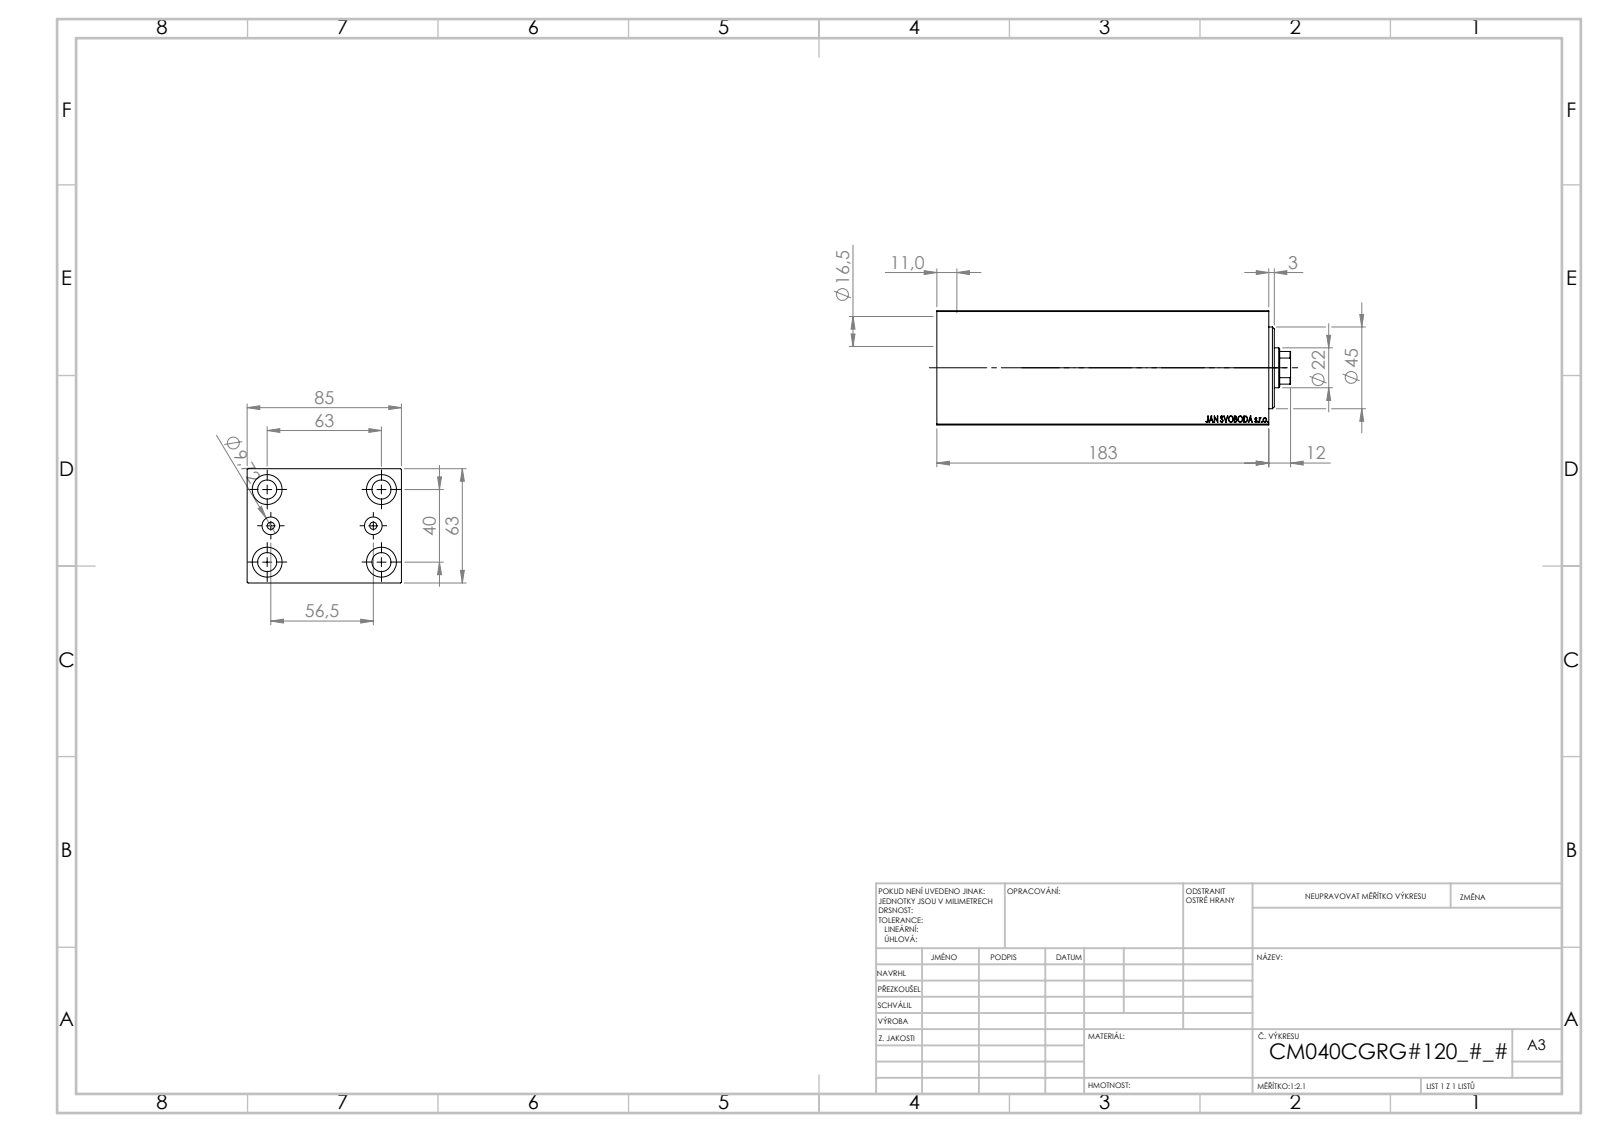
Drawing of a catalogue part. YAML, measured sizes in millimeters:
part_name: "V450CM_VC_B; V450CM_C_Body; V450CM_C_VCP"
step_written_by: "SolidWorks 2019 (CONFIG_CONTROL_DESIGN)"
units: millimeters
bodies: {solids: 3, faces: 858, planar: 408, cylindrical: 56, other: 394}
overall_size: [195, 85, 63]
volume: 799276
surface_area: 139803
round_holes:
  - {diameter: 10.5, count: 4}
  - {diameter: 16.5, count: 4}
  - {diameter: 4, count: 2}
  - {diameter: 9.72, count: 2}
  - {diameter: 12.5, count: 1}
  - {diameter: 22, count: 1}
  - {diameter: 25.5, count: 1}
  - {diameter: 40, count: 1}
  - {diameter: 42, count: 1}
  - {diameter: 45, count: 1}
partial_cylinders:
  - {radius: 10.5, count: 1}
face_to_face_distances: [63, 85, 12, 171, 183, 1, 159, 11, 172, 160]
hole_center_spacings: [37.31, 20.1, 20.5, 40, 61.82, 63, 64.2, 74.63]
